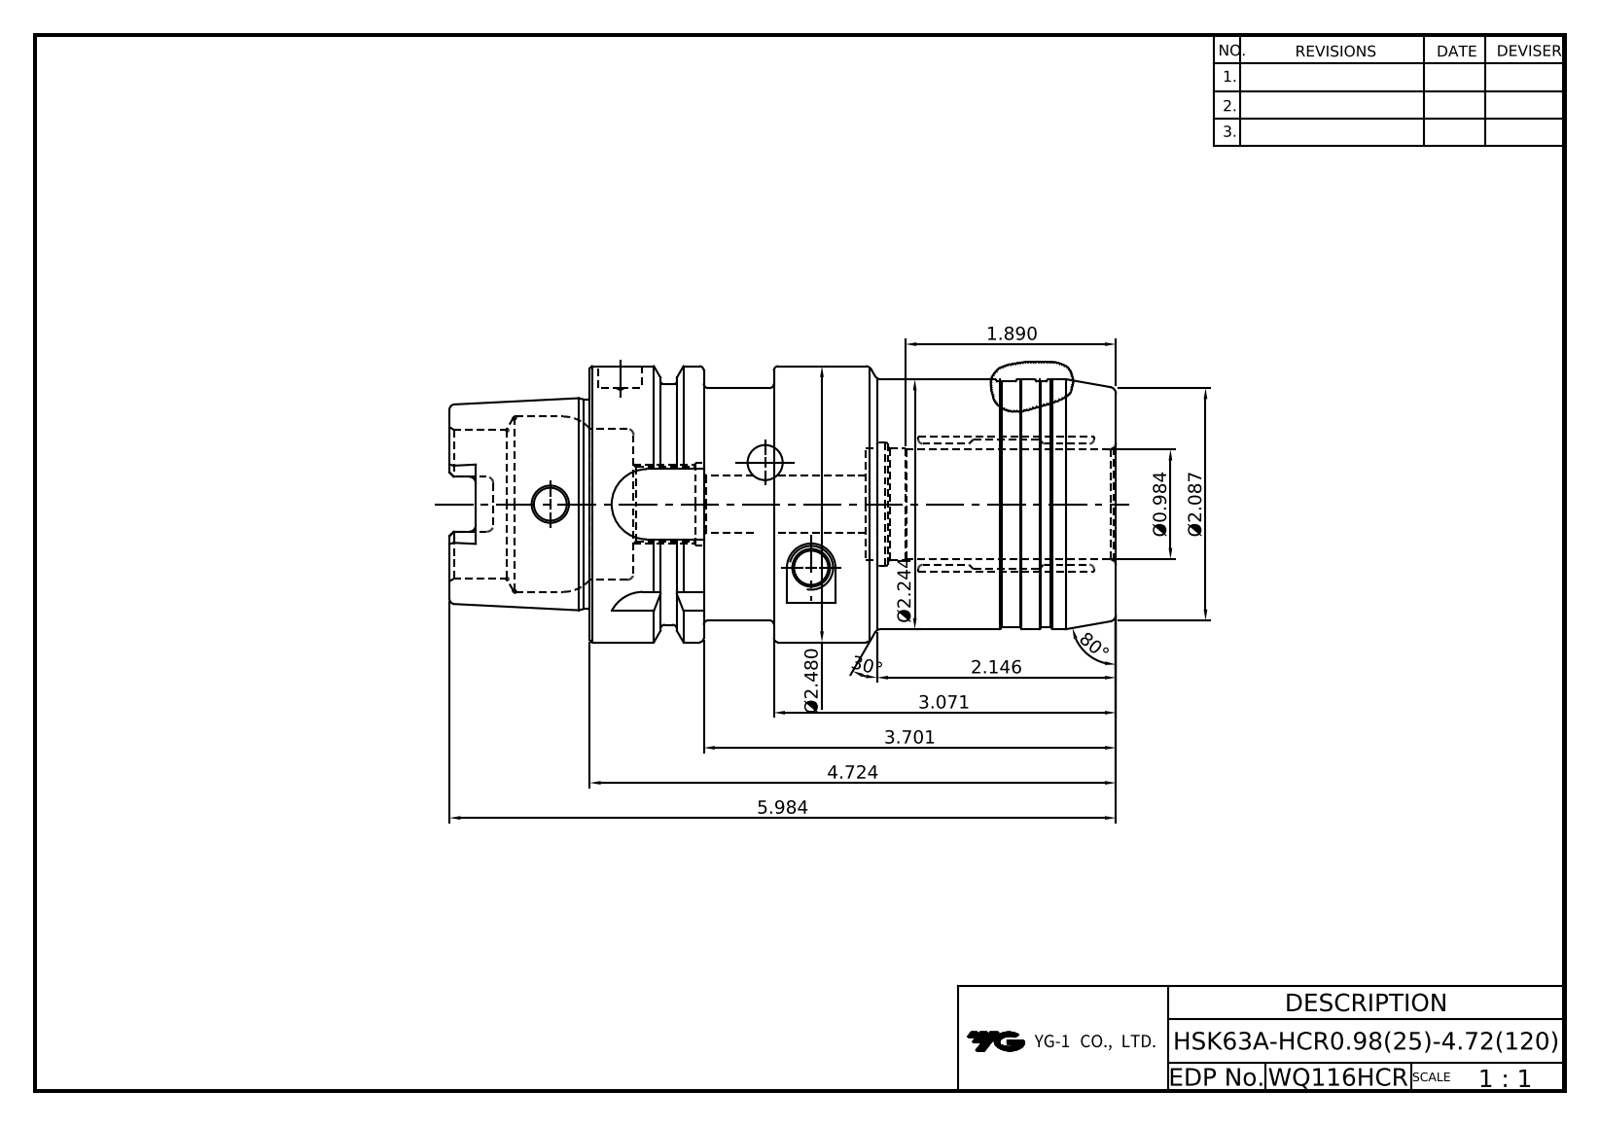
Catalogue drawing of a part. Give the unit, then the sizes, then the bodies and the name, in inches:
Units: inches
Overall size (bounding box): 5.984 × 2.48 × 2.48
Round holes (diameter × count): ⌀0.295 ×1, ⌀0.394 ×1, ⌀0.52 ×1, ⌀0.666 ×1, ⌀0.748 ×1, ⌀0.984 ×1, ⌀1.008 ×1, ⌀1.339 ×1, ⌀1.575 ×1
Round bosses / shafts (diameter × count): ⌀2.48 ×1, ⌀2.244 ×1, ⌀2.205 ×1, ⌀2.165 ×1, ⌀2.087 ×1, ⌀1.891 ×1
Partial cylindrical surfaces — rounded edges, fillets, slot ends (radius × count): R0.059 ×6, R0.113 ×4, R0.315 ×4
Main face-to-face distances: 4.724, 0.63, 1.26, 1.654, 1.024, 2.087, 3.701, 0.394, 4.331, 3.071
Volume: 17.84 in³ · Surface area: 71.74 in²
Bodies: 1 solid, 144 faces (44 planar, 39 cylindrical, 61 other)
Part name (STEP PRODUCT): LO-HSK63A-HCR25-120
STEP written by: Autodesk Inventor 2020 (AUTOMOTIVE_DESIGN)
